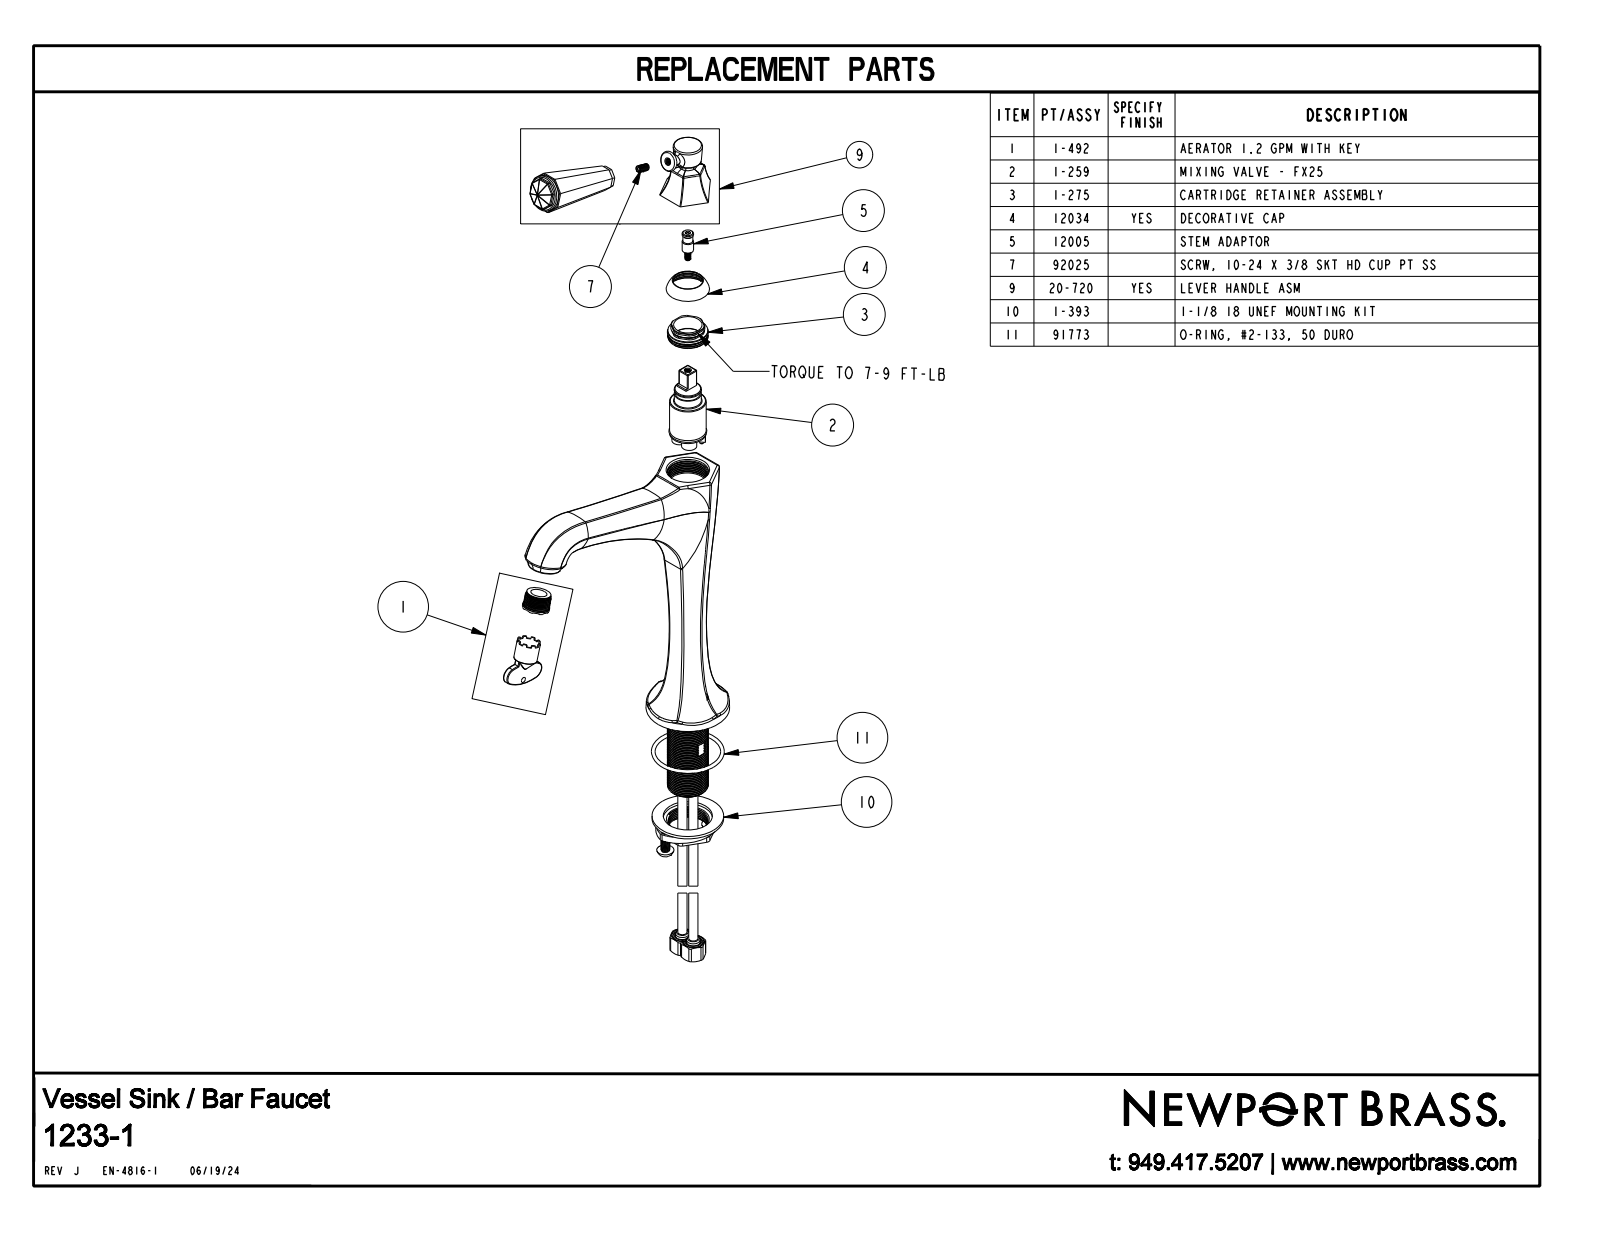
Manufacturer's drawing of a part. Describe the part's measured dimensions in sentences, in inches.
The part is named "1233-1". Its 3-D file was written by "CREO PARAMETRIC BY PTC INC, 2018400 (AUTOMOTIVE_DESIGN)". It is 1 solid with 241 faces: 69 planar, 26 cylindrical and 146 other. Overall it measures 10.583 by 7.241 by 2.3 inches. Its volume is 20.06 cubic inches and its surface area 77.71 square inches. Round bosses or shafts: 1 of diameter 0.98. Partial cylindrical surfaces (rounded edges, fillets, slot ends): 24 of radius 0.03. The main face-to-face distances are 8, 8.063, 0.063, 0.585, 2.563, 0.8, 0.354, 0.1, 2.463, 0.115.
